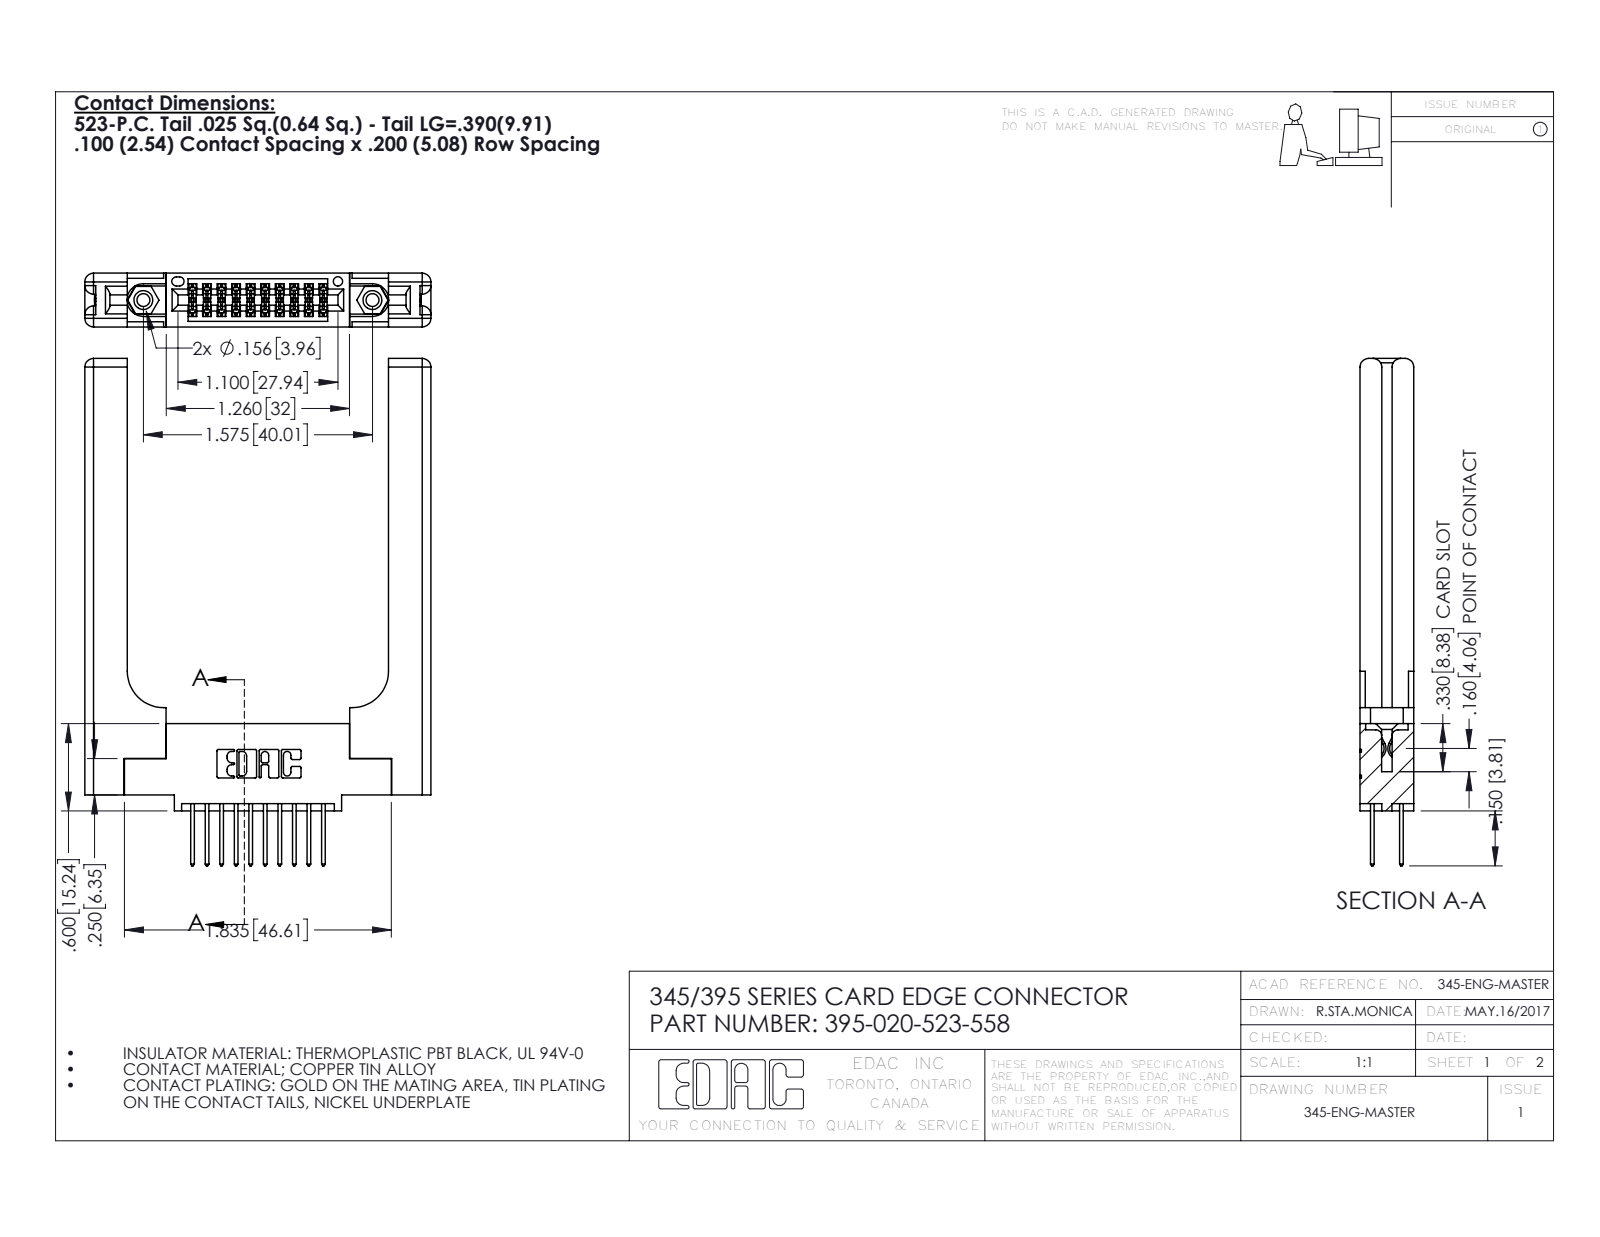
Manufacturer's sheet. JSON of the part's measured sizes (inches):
{"part_name": "345 Part_0.110 Offset - 0.156 Dia-TH; 395-020-523-558; 345-250-001_345-250-001-102; 345-292-001_345-293-123 (+1 more)", "step_written_by": "SolidWorks 2016 (CONFIG_CONTROL_DESIGN)", "units": "inches", "bodies": {"solids": 25, "faces": 1386, "planar": 892, "cylindrical": 434, "other": 60}, "overall_size": [3.487, 2.379, 0.37], "volume_in3": 0.855, "surface_area_in2": 20, "round_holes": [[0.089, 2], [0.125, 2], [0.156, 2], [0.064, 1]], "round_bosses_or_shafts": [[0.155, 2]], "partial_cylinders_radius": [[0.006, 30], [0.01, 22], [0.01, 20], [0.06, 16], [0.007, 6], [0.031, 6], [0.026, 3], [0.014, 2]], "face_to_face_distances": [0.37, 0.072, 0.298, 0.148, 0.15, 0.077, 0.22, 0.2, 0.225, 0.098], "hole_center_spacings": [0.27, 1.344, 1.575]}
